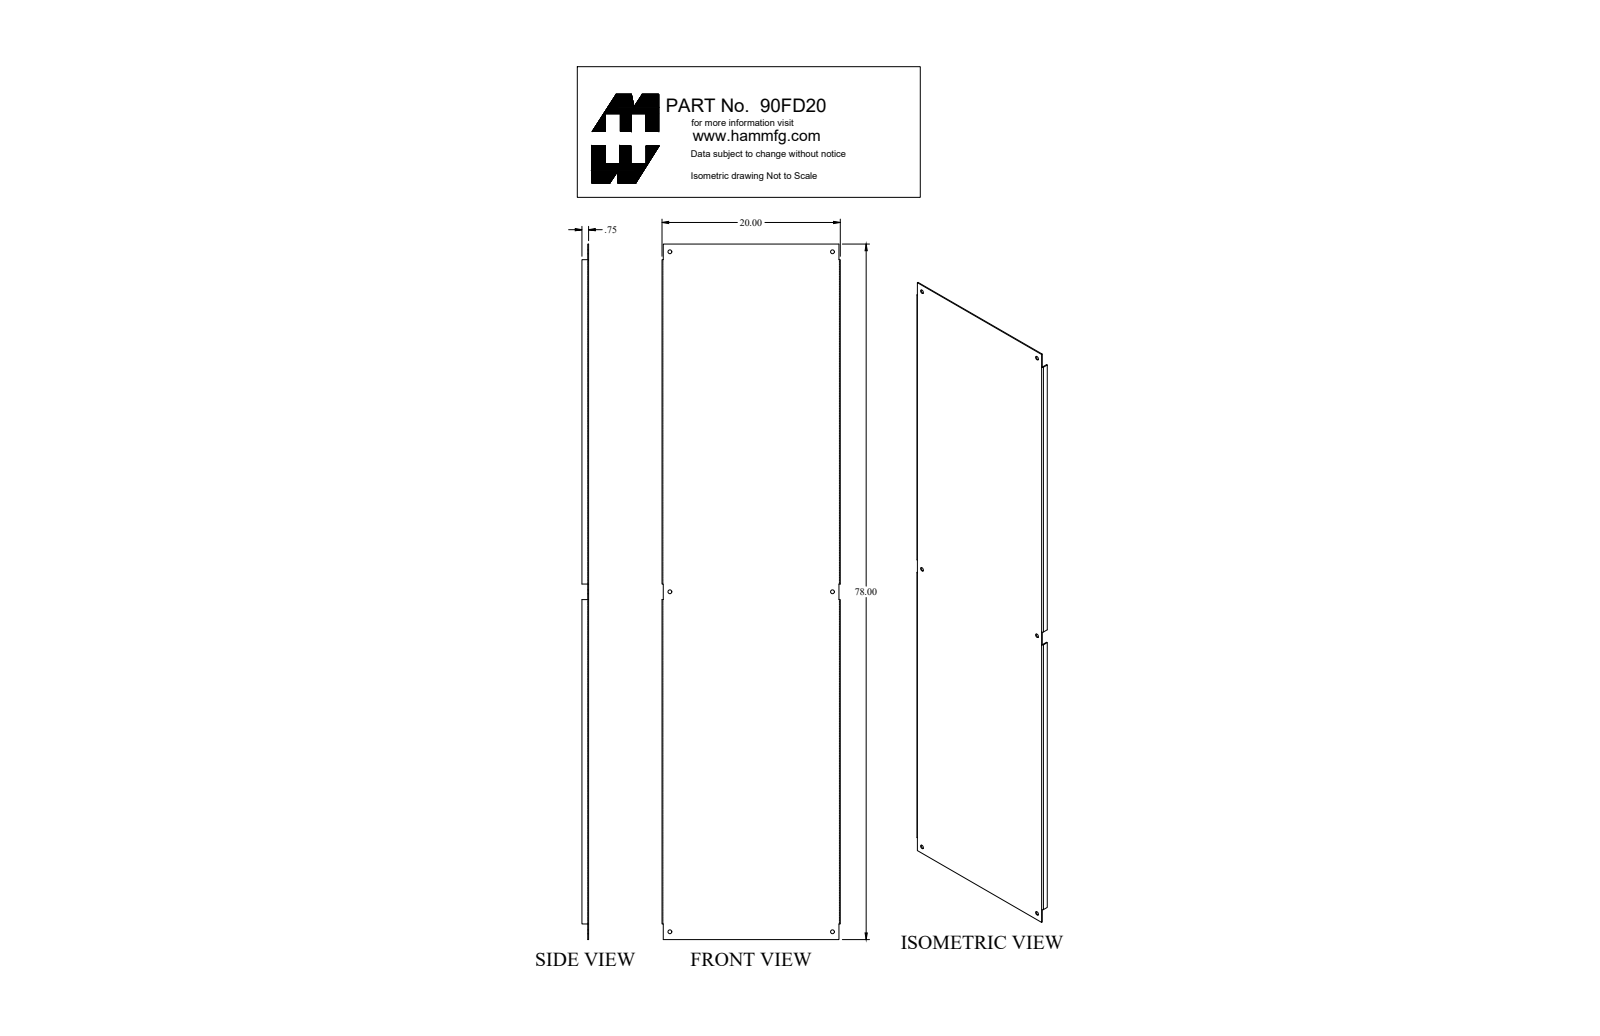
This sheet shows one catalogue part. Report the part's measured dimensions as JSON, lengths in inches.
{"part_name": "90FD20_Default", "step_written_by": "SolidWorks 2018 (CONFIG_CONTROL_DESIGN)", "units": "inches", "bodies": {"solids": 1, "faces": 50, "planar": 30, "cylindrical": 20, "other": 0}, "overall_size": [78, 20, 0.75], "volume_in3": 156.5, "surface_area_in2": 3314, "round_holes": [[0.437, 6]], "partial_cylinders_radius": [[0.048, 2], [0.143, 2]], "face_to_face_distances": [0.095, 19.905, 19.81, 20, 0.75, 0.655, 78, 0.143, 19.857, 0.048], "hole_center_spacings": [38.125, 42.268, 18.25, 76.25, 78.404]}
